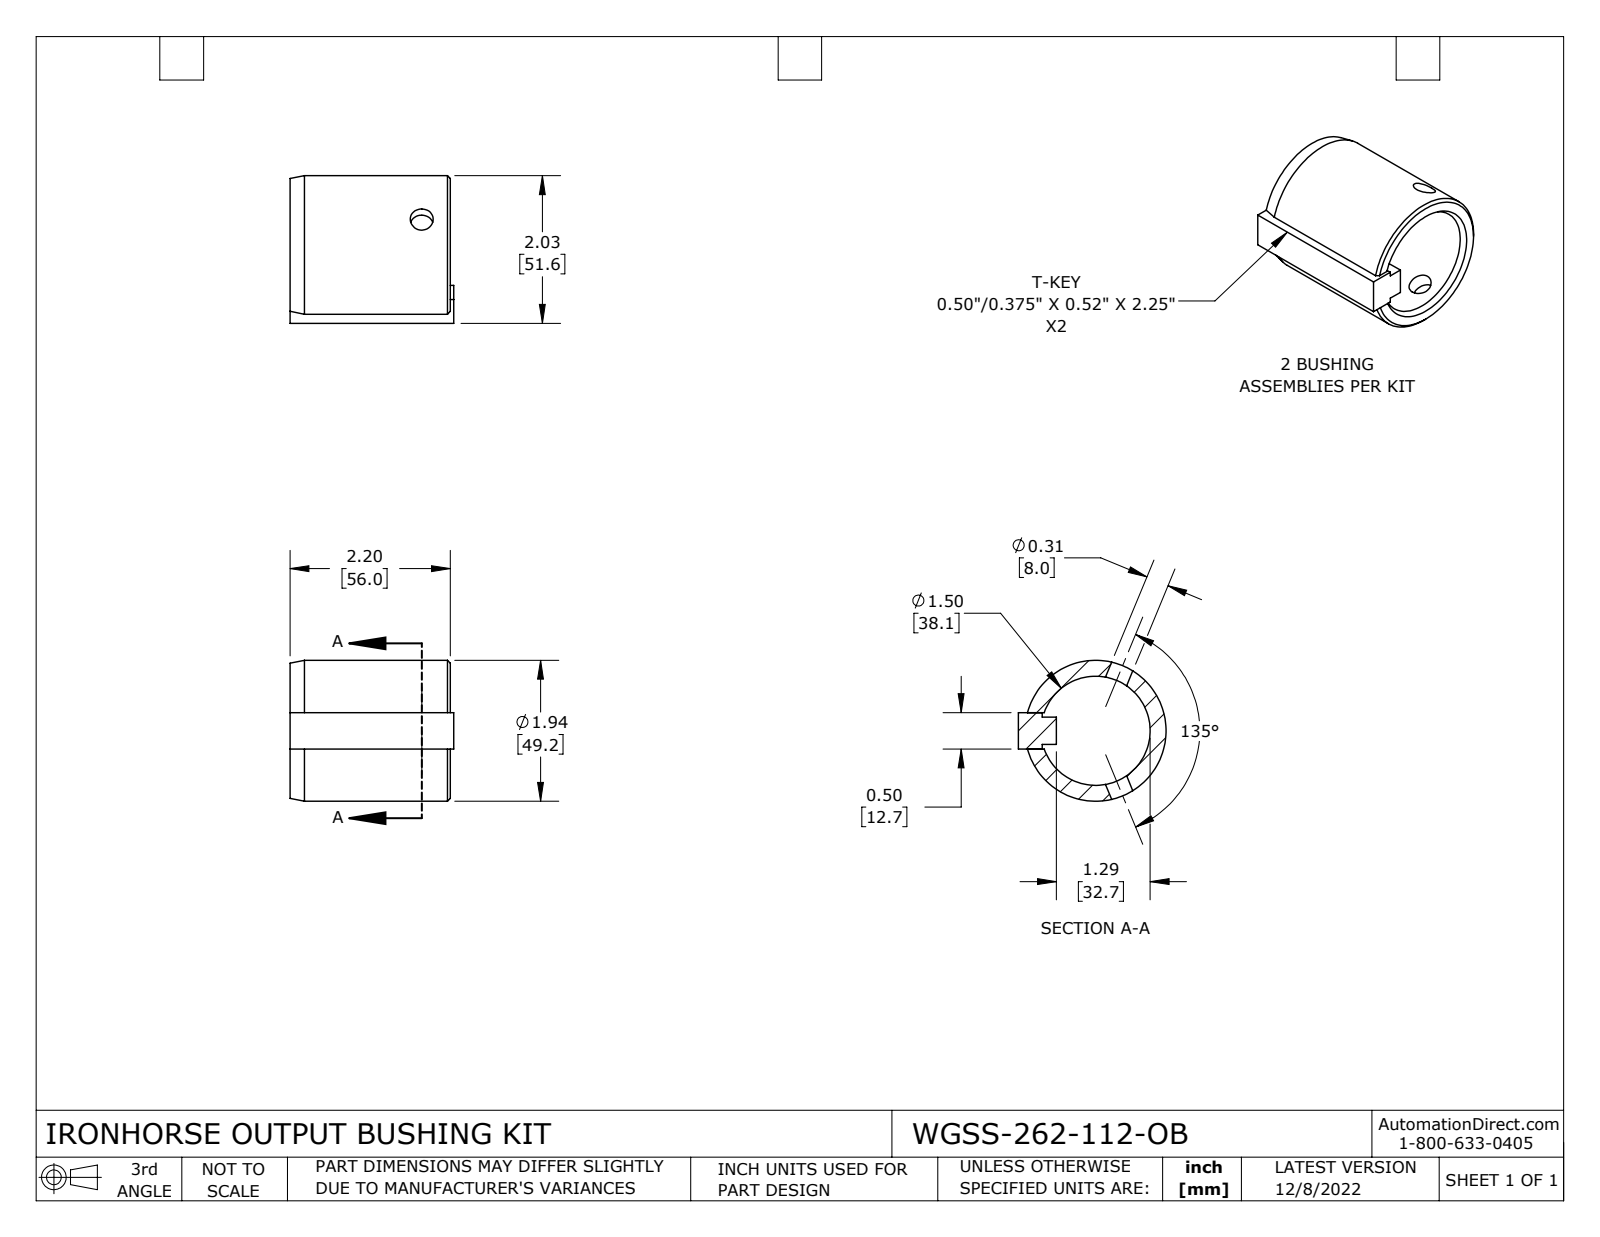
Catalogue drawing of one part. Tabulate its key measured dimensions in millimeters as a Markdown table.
| quantity | value |
| --- | --- |
| part name | WGSS-262-112-OB |
| STEP written by | SolidWorks 2021 (CONFIG_CONTROL_DESIGN) |
| units | millimeters |
| bodies | 2 solids, 33 faces (14 planar, 10 cylindrical, 9 other) |
| overall size | 57.15 × 51.57 × 49.21 |
| volume | 46 164 mm³ |
| surface area | 18 894 mm² |
| round holes (diameter × count) | 8 × 2, 38.1 × 1 |
| round bosses / shafts (diameter × count) | 49.21 × 1 |
| main face-to-face distances | 12.7, 13.27, 56, 1.59, 11.11, 11.12, 9.53, 1.58, 4.96, 8.31 |
